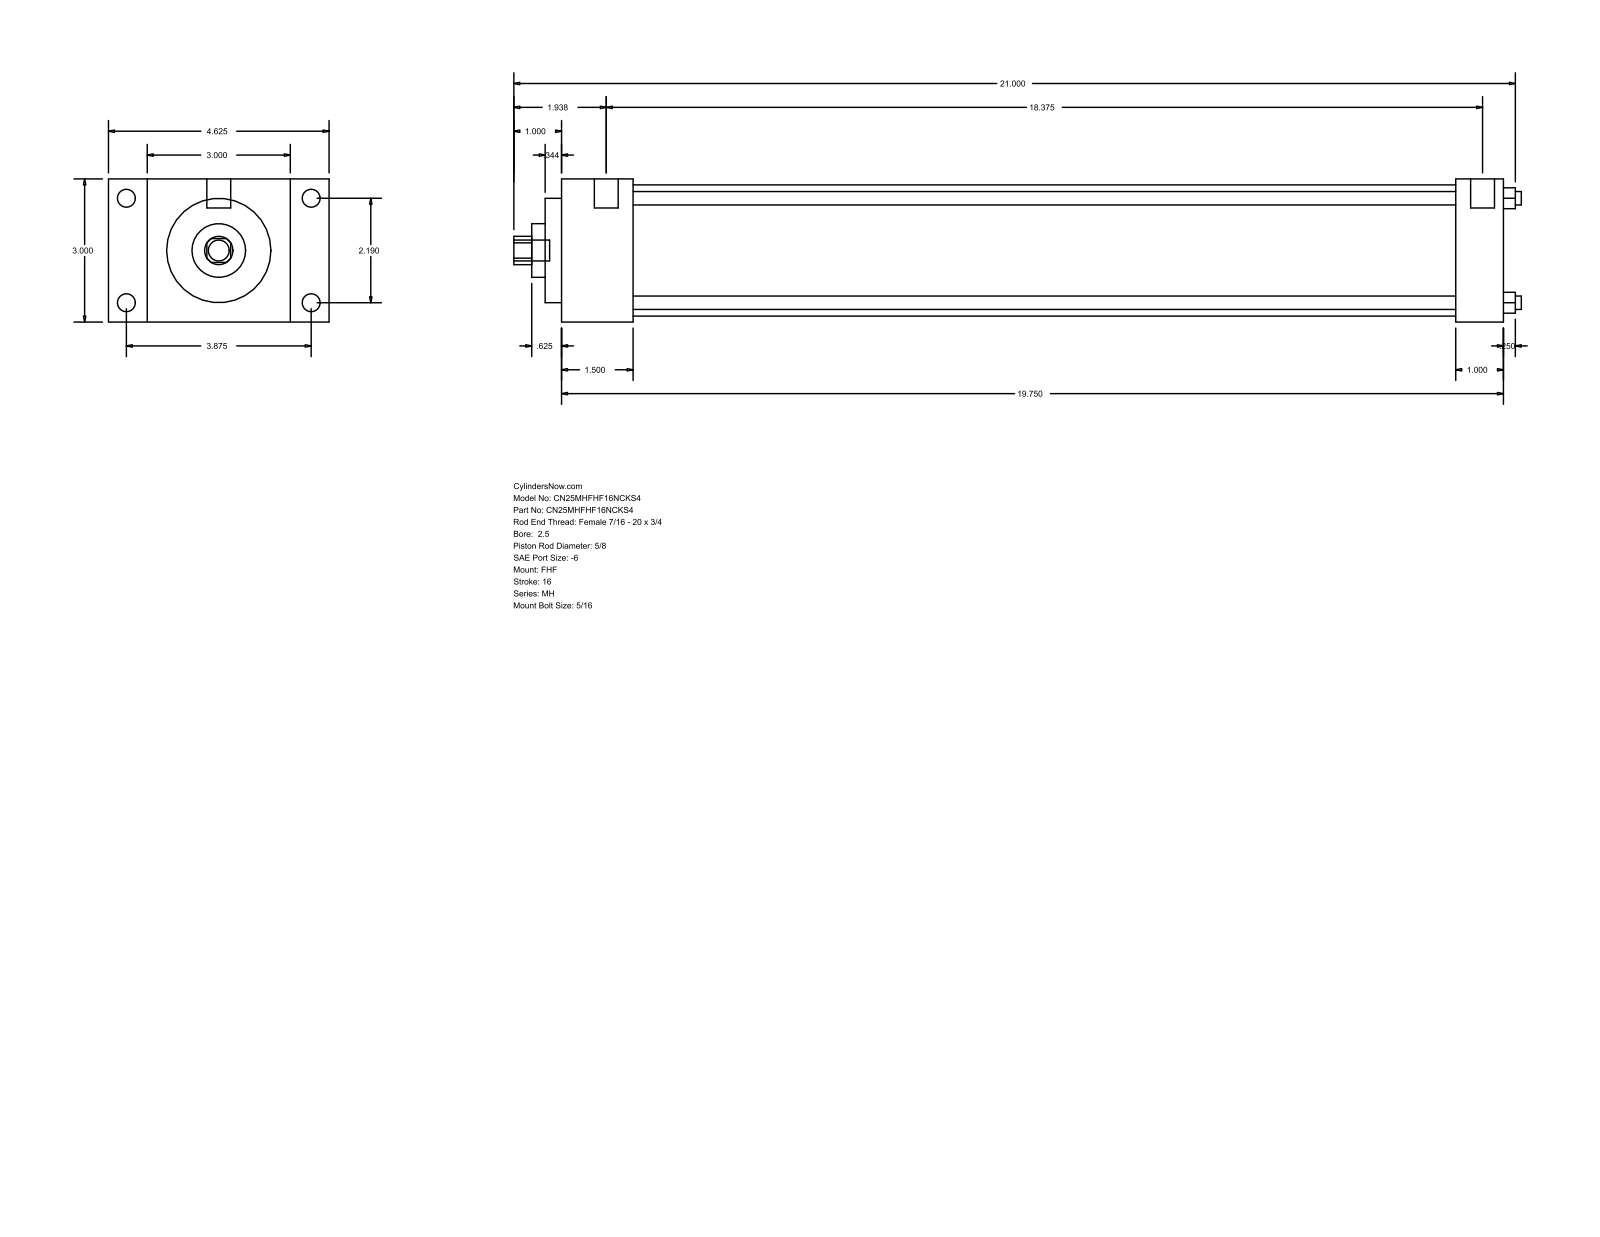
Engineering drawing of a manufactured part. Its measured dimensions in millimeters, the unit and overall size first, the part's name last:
Units: millimetres
Overall size (bounding box): 536.58 × 117.47 × 76.2
Round holes (diameter × count): ⌀7.14 ×4, ⌀15.88 ×1, ⌀28.57 ×1, ⌀55.55 ×1, ⌀69.85 ×1
Round bosses / shafts (diameter × count): ⌀9.53 ×4, ⌀5.56 ×4, ⌀12.7 ×2, ⌀11.11 ×1
Partial cylindrical surfaces — rounded edges, fillets, slot ends (radius × count): R7.54 ×1
Main face-to-face distances: 76.2, 501.65, 38.1, 463.55, 20.64, 96.84, 117.48, 25.4, 476.25, 438.15
Hole centre spacings: 39.33, 55.62, 78.66
Bodies: 0 solids, 90 faces (61 planar, 29 cylindrical, 0 other)
Part name (STEP PRODUCT): MH_FHF__0250_0.625
STEP written by: GSSL Pune (CONFIG_CONTROL_DESIGN)
